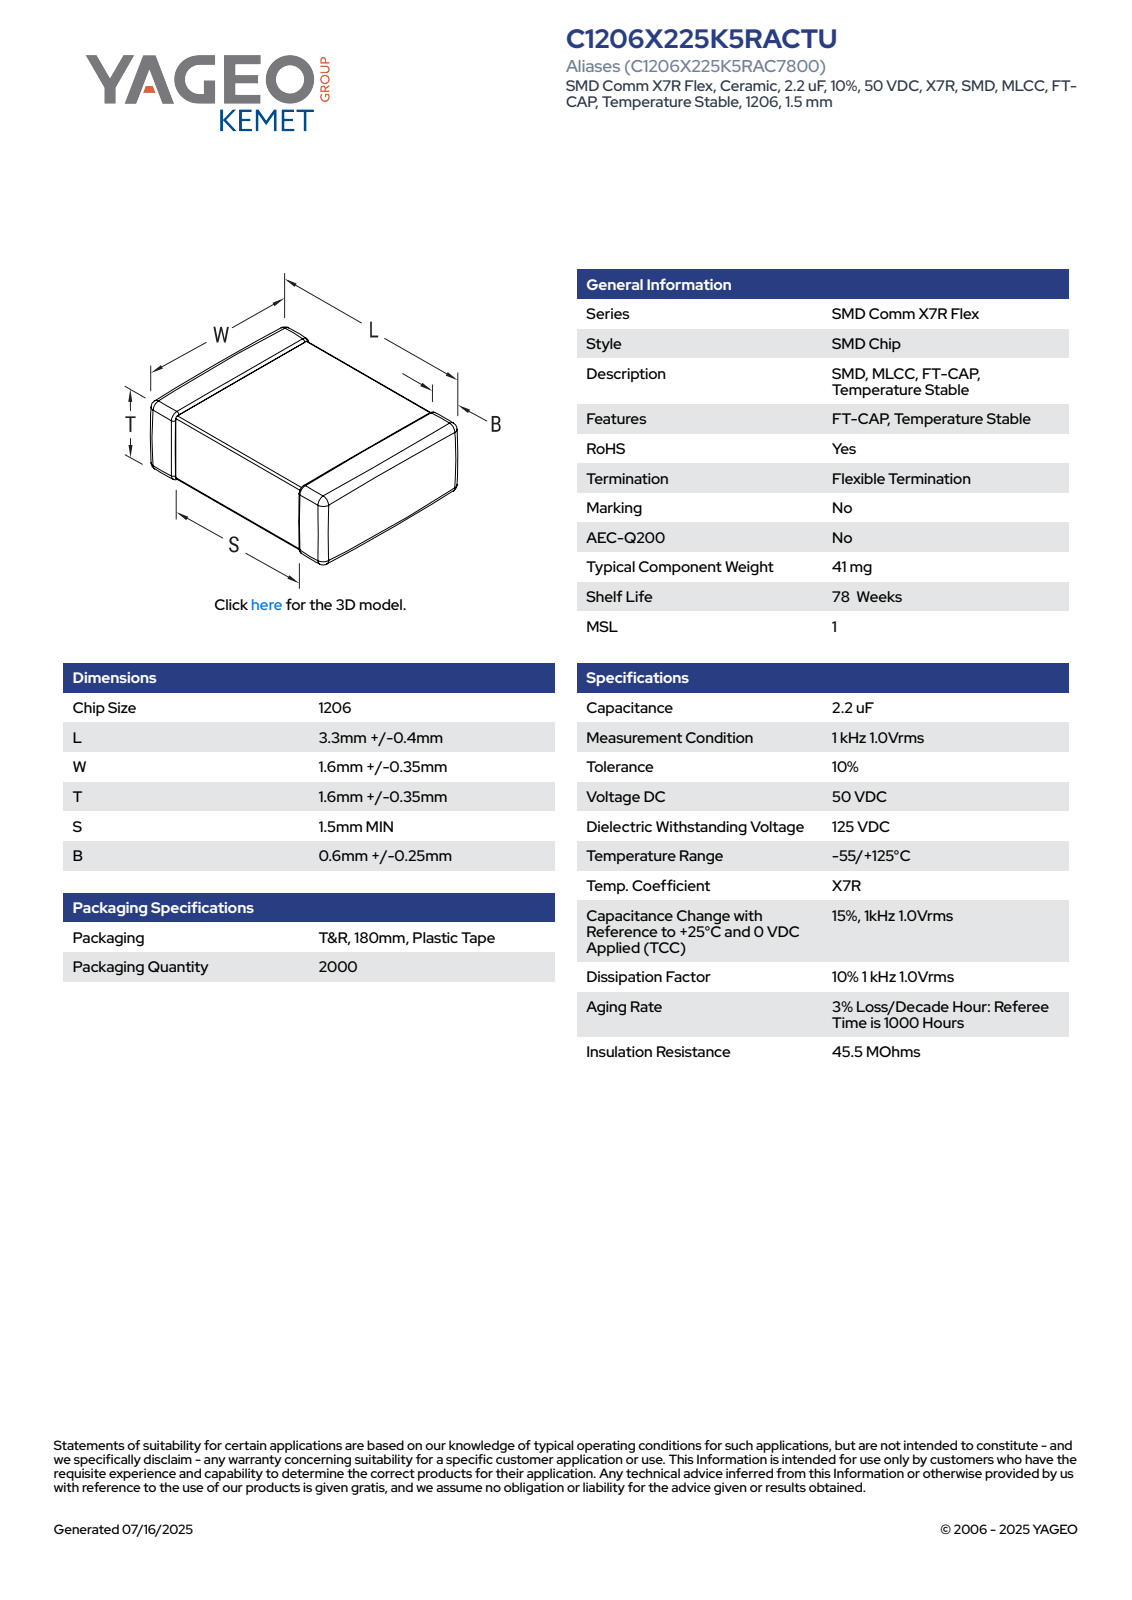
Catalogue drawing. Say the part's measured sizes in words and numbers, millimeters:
The part is named "CCS_CCSTD_1206_L3.7W1.95T1.8B0.6". Its 3-D file was written by "SolidWorks 2021 (AUTOMOTIVE_DESIGN)". It is 4 solids with 129 faces: 71 planar, 42 cylindrical and 16 other. Overall it measures 3.7 by 1.95 by 1.8 millimeters. Its volume is 12 cubic millimeters and its surface area 34 square millimeters. The main face-to-face distances are 1.76, 1.91, 1.72, 1.87, 3.7, 1.8, 1.95, 1.71, 1.99, 2.
